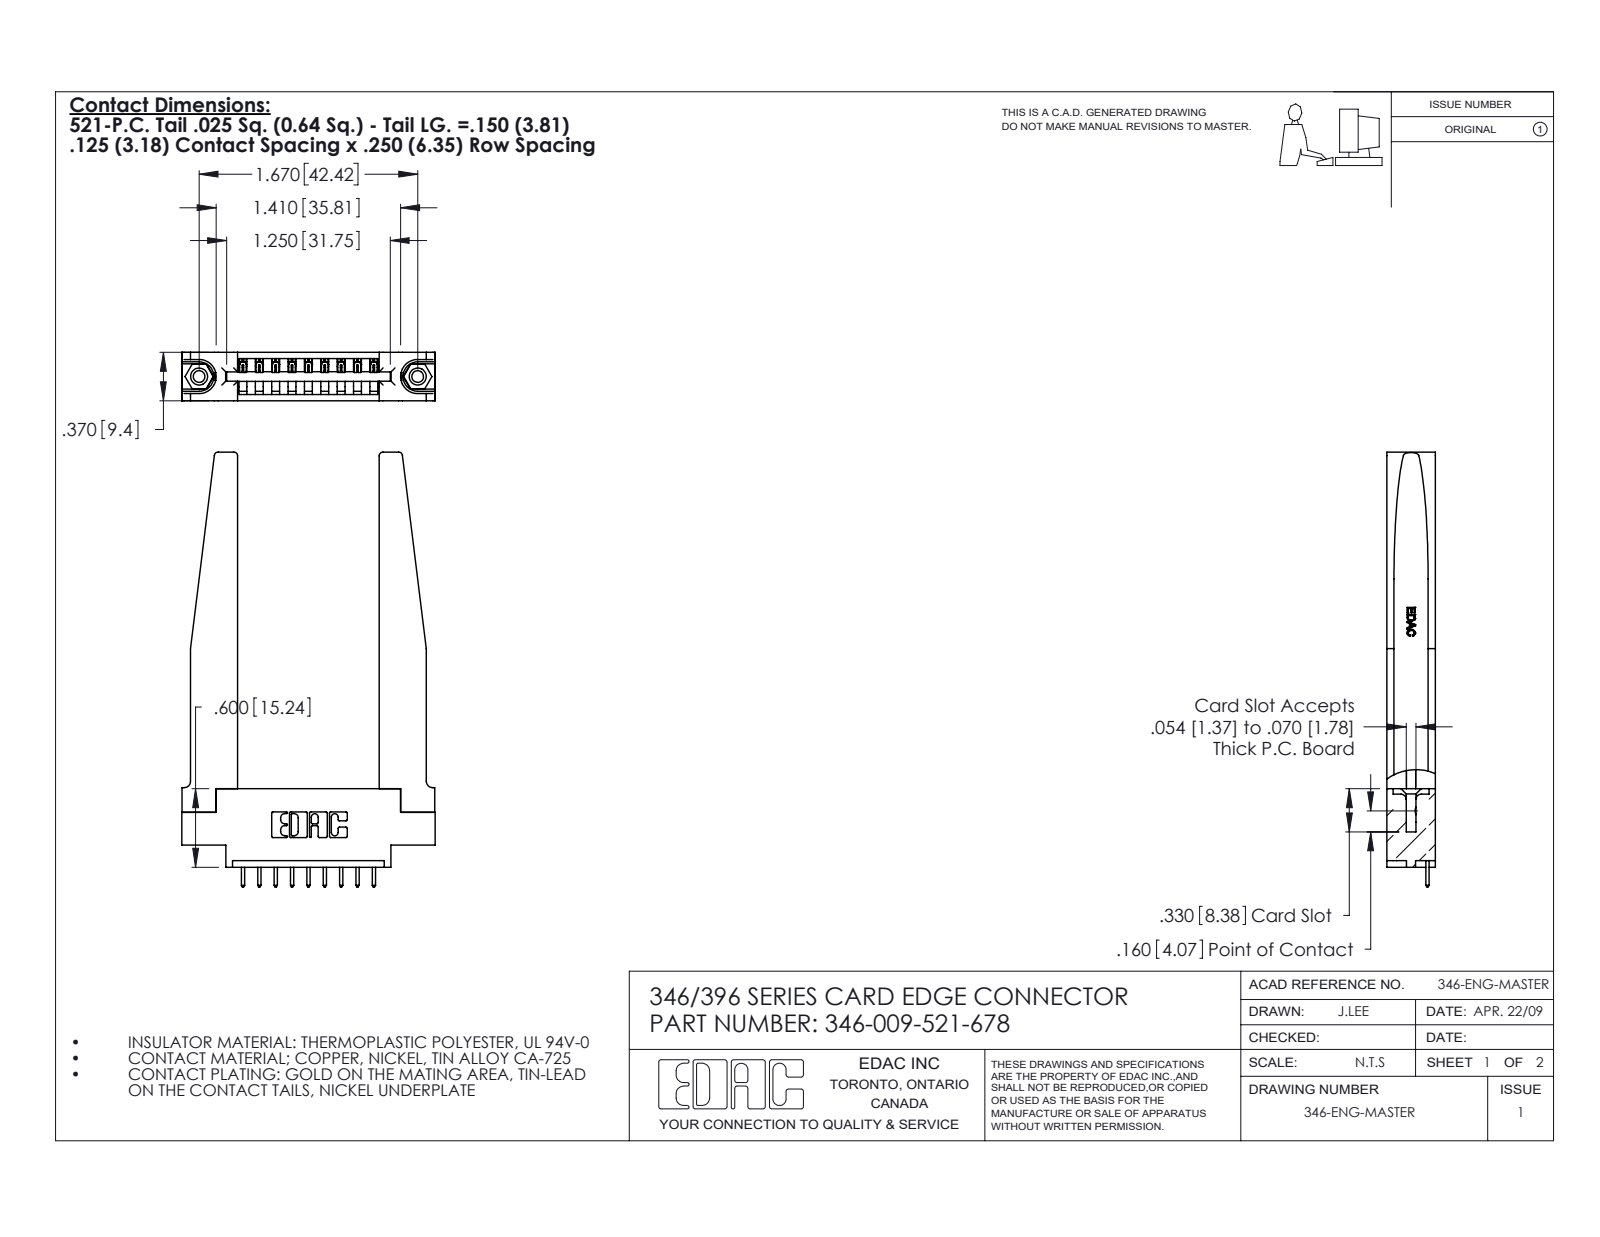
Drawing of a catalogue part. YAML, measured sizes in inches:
part_name: "345-292-001_345-293-121; 346-220-078_345-220-078; 346-009-521-678; 345-250-001_345-250-001-102 (+1 more)"
step_written_by: "SolidWorks 2020 (CONFIG_CONTROL_DESIGN)"
units: inches
bodies: {solids: 14, faces: 896, planar: 596, cylindrical: 248, other: 52}
overall_size: [3.32, 1.935, 0.37]
volume: 0.683
surface_area: 18.02
round_holes:
  - {diameter: 0.089, count: 2}
  - {diameter: 0.125, count: 2}
  - {diameter: 0.156, count: 2}
  - {diameter: 0.064, count: 1}
round_bosses_or_shafts:
  - {diameter: 0.155, count: 2}
partial_cylinders:
  - {radius: 0.01, count: 22}
  - {radius: 0.006, count: 18}
  - {radius: 0.01, count: 18}
  - {radius: 0.03, count: 8}
  - {radius: 0.007, count: 6}
  - {radius: 0.031, count: 6}
  - {radius: 0.026, count: 3}
  - {radius: 0.031, count: 2}
face_to_face_distances: [0.37, 0.15, 0.22, 0.148, 0.072, 0.25, 0.048, 0.322, 0.102, 0.173]
hole_center_spacings: [0.246, 1.465, 1.67]
